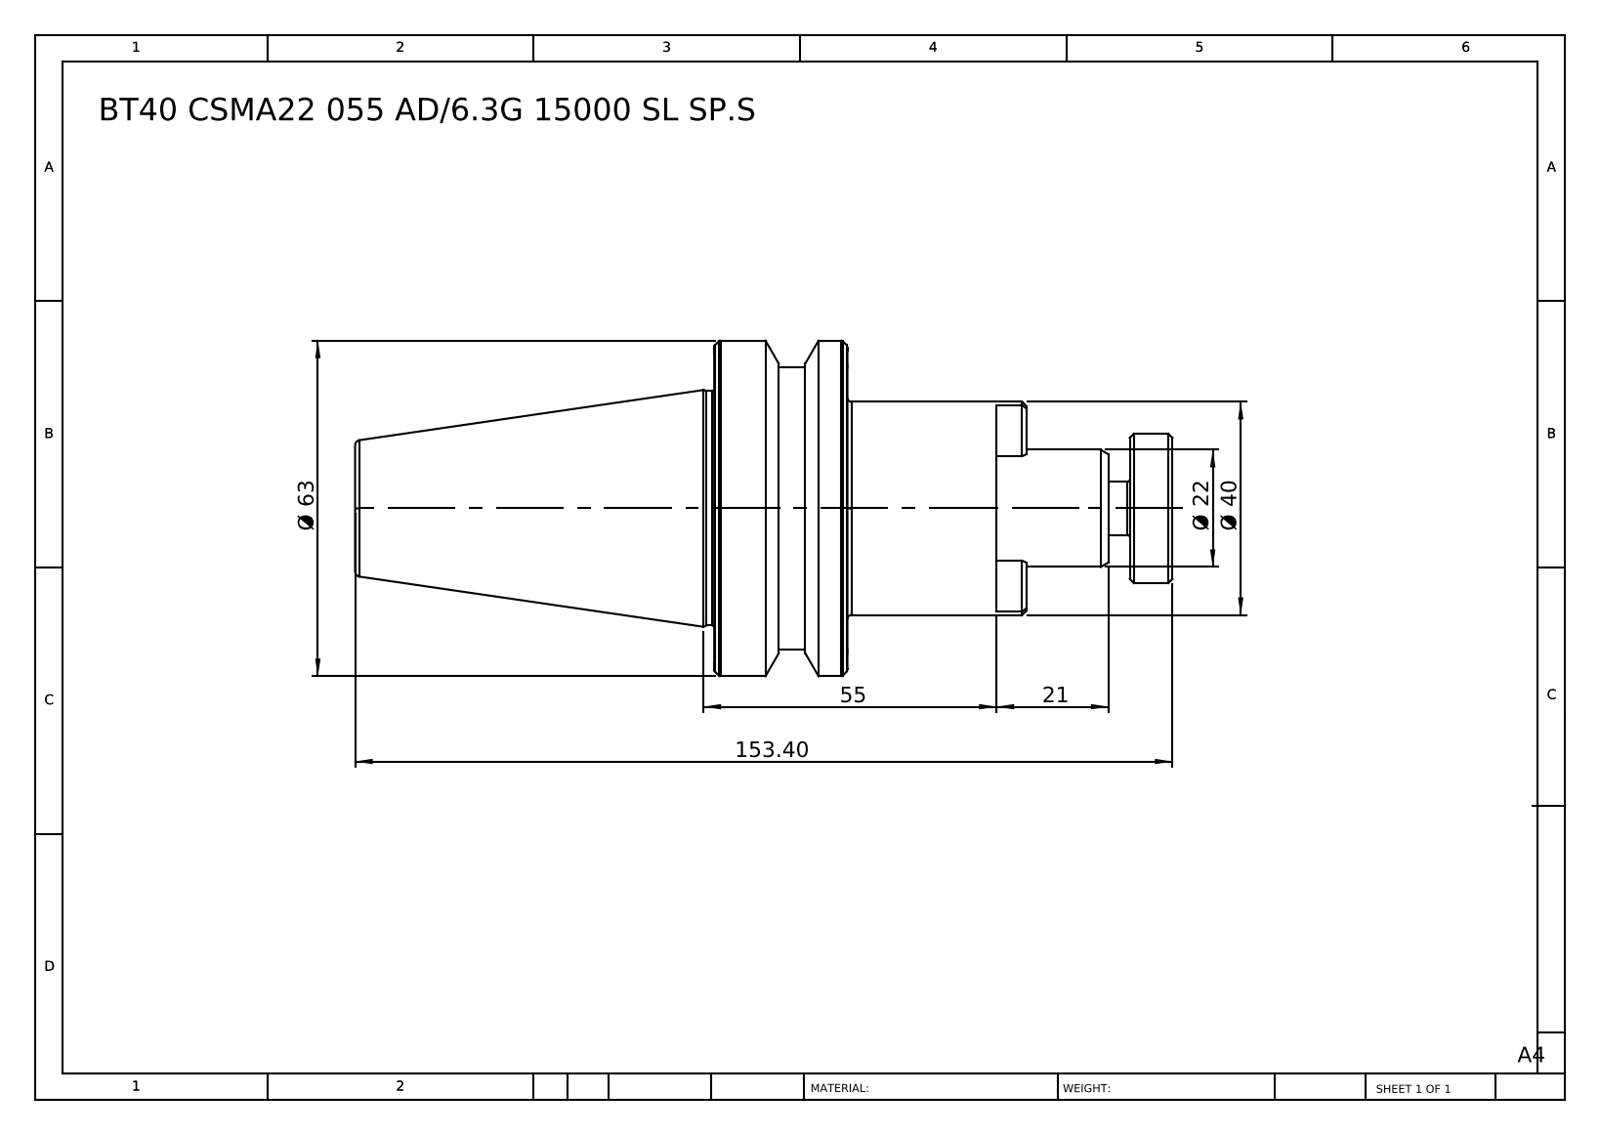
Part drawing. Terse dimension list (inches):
name: BT40 CSMA22 055 AD 6.3G15000 SL SP.S
written by: SolidWorks 2014 (CONFIG_CONTROL_DESIGN)
unit: in
bodies: 1 solid, 78 faces (20 planar, 16 cylindrical, 42 other)
size: 6.039 × 2.48 × 2.48
volume: 11.46 in³; area: 39.08 in²
bosses: 1× ⌀2.48, 1× ⌀2.087, 1× ⌀1.732, 1× ⌀1.575, 1× ⌀1.102, 1× ⌀0.866, 1× ⌀0.394
face distances: 0.984, 2.087, 1.102, 1.299, 2.402, 3.386, 0.315, 3.071, 6.039, 5.724
